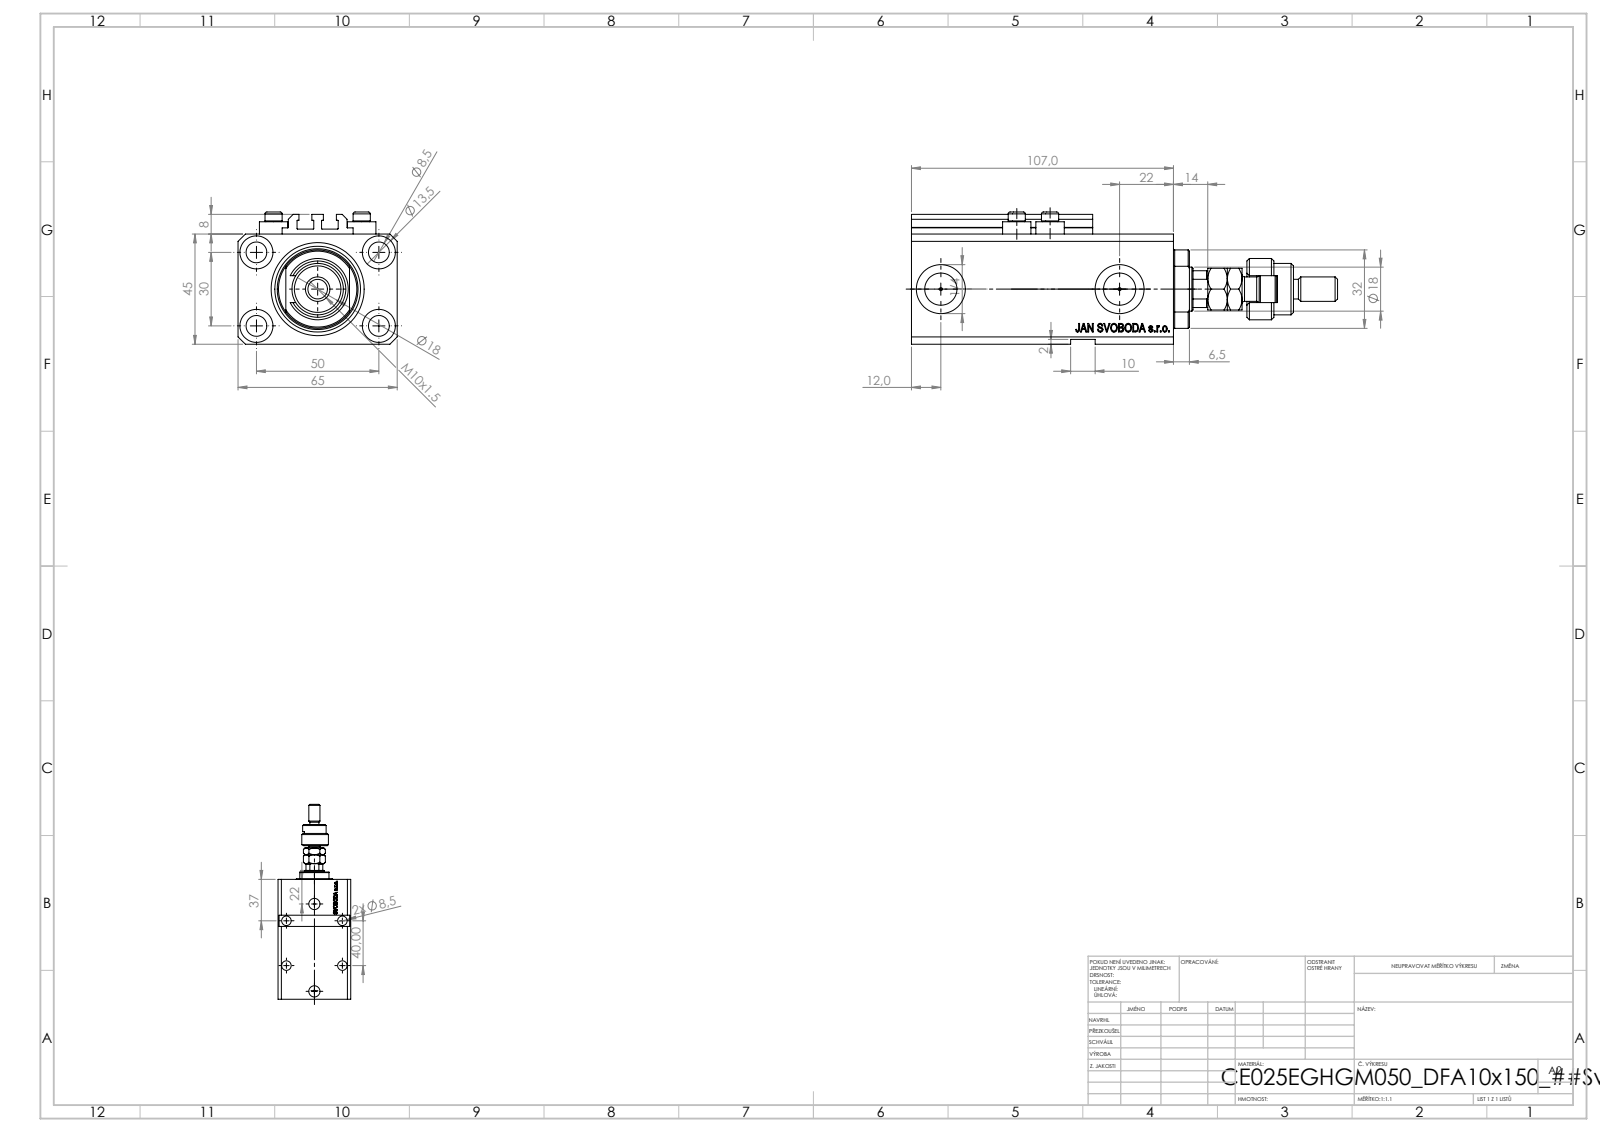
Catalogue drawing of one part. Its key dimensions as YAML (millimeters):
part_name: "FEMALE_PART_FOR_DFA; V250CE_C_VCP; V250CE_VC_E; ALLEN BOLT V250CE (+2 more)"
step_written_by: "SolidWorks 2019 (CONFIG_CONTROL_DESIGN)"
units: millimeters
bodies: {solids: 10, faces: 1172, planar: 539, cylindrical: 159, other: 474}
overall_size: [174, 65, 54]
volume: 285194
surface_area: 82321
round_holes:
  - {diameter: 8.5, count: 9}
  - {diameter: 1.25, count: 4}
  - {diameter: 4, count: 4}
  - {diameter: 13.5, count: 4}
  - {diameter: 10, count: 2}
  - {diameter: 13.16, count: 2}
  - {diameter: 20, count: 2}
  - {diameter: 18, count: 1}
  - {diameter: 38, count: 1}
round_bosses_or_shafts:
  - {diameter: 11.6, count: 4}
  - {diameter: 7, count: 4}
  - {diameter: 25, count: 1}
  - {diameter: 21, count: 1}
  - {diameter: 16, count: 1}
  - {diameter: 10, count: 1}
  - {diameter: 8, count: 1}
partial_cylinders:
  - {radius: 0.2, count: 10}
  - {radius: 5.5, count: 1}
  - {radius: 8.5, count: 1}
  - {radius: 8.75, count: 1}
  - {radius: 16, count: 1}
face_to_face_distances: [45, 65, 14, 2, 93, 47, 107, 2.5, 3, 10]
hole_center_spacings: [29.15, 50, 13.6, 14.76, 15.12, 27.51, 27.89, 30]
